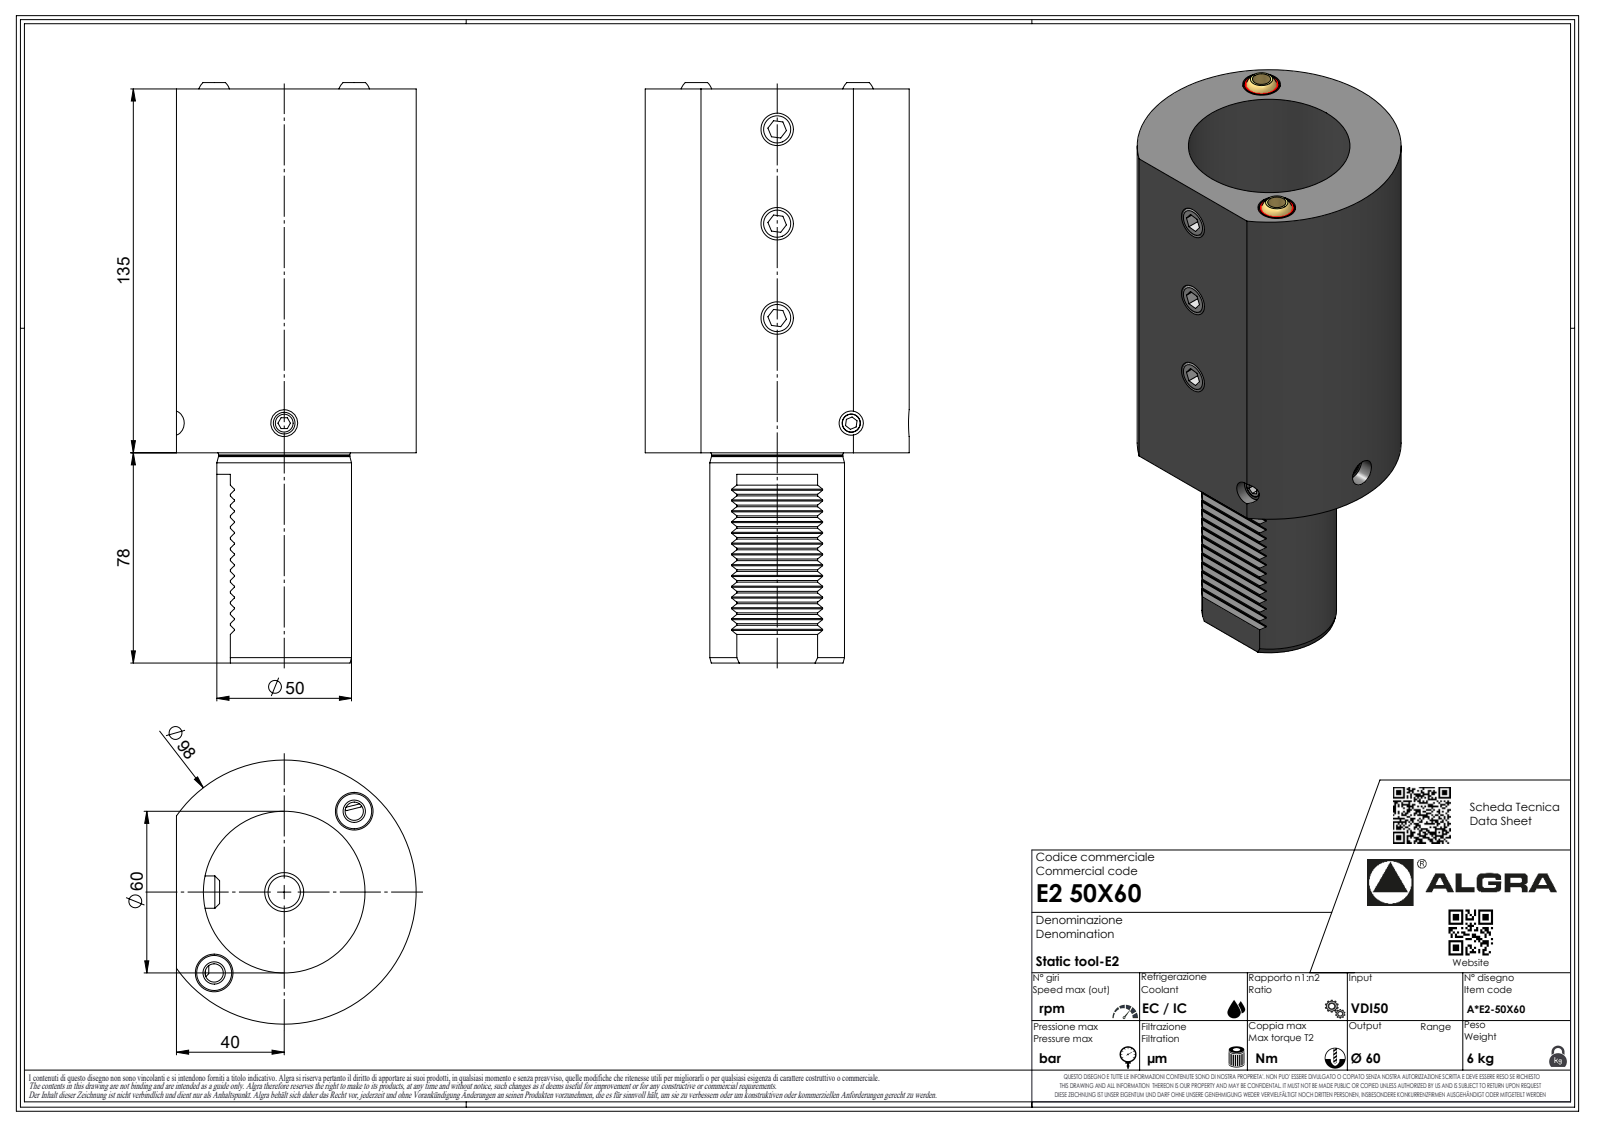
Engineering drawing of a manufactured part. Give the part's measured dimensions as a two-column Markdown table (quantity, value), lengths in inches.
| quantity | value |
| --- | --- |
| part name | E250X60 |
| STEP written by | SolidWorks 2023 (AUTOMOTIVE_DESIGN) |
| units | inches |
| bodies | 1 solid, 285 faces (188 planar, 44 cylindrical, 53 other) |
| overall size | 8.479 × 3.858 × 3.504 |
| volume | 49.14 in³ |
| surface area | 138 in² |
| round holes (diameter × count) | 0.083 × 1, 2.362 × 1 |
| round bosses / shafts (diameter × count) | 3.858 × 1, 1.969 × 1, 1.917 × 1, 0.251 × 1, 0.067 × 1 |
| partial cylindrical surfaces (radius × count) | 0.012 × 14, 0.013 × 7, 0.02 × 7, 0.146 × 7, 0.008 × 1 |
| main face-to-face distances | 5.315, 0.984, 4.331, 3.071, 4.055, 8.386, 0.111, 0.557, 0.445, 0.223 |
